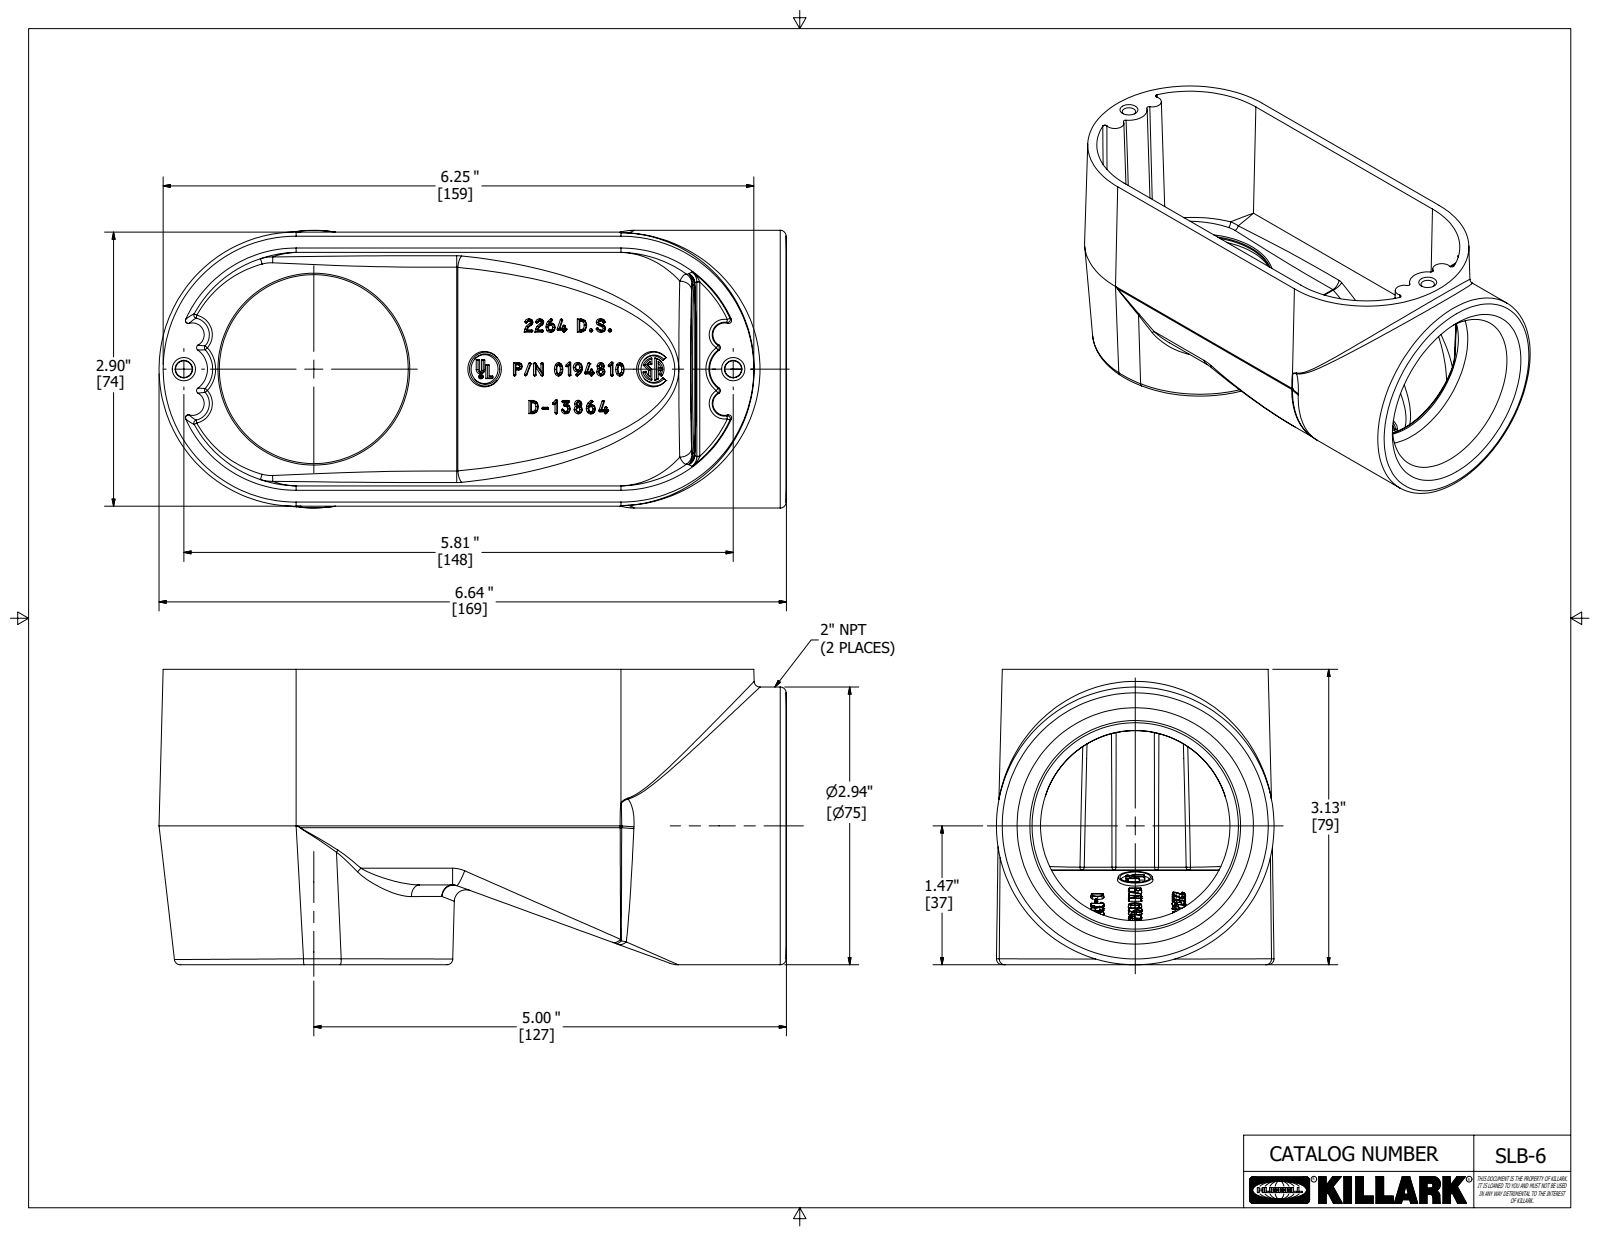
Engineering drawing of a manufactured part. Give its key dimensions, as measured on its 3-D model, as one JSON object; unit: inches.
{"part_name": "0194810 -2", "step_written_by": "Autodesk Inventor 2020 (AUTOMOTIVE_DESIGN)", "units": "inches", "bodies": {"solids": 1, "faces": 645, "planar": 194, "cylindrical": 13, "other": 438}, "overall_size": [6.637, 3.125, 2.938], "volume_in3": 13.11, "surface_area_in2": 116.6, "round_bosses_or_shafts": [[2.937, 1]], "partial_cylinders_radius": [[0.031, 2], [0.25, 2], [0.004, 1], [0.125, 1], [1.002, 1], [1.235, 1], [1.45, 1]], "face_to_face_distances": [2.688, 0.156, 2.124, 1.002, 3.125, 2.813, 1.811, 0.313, 0.845, 0.156]}
